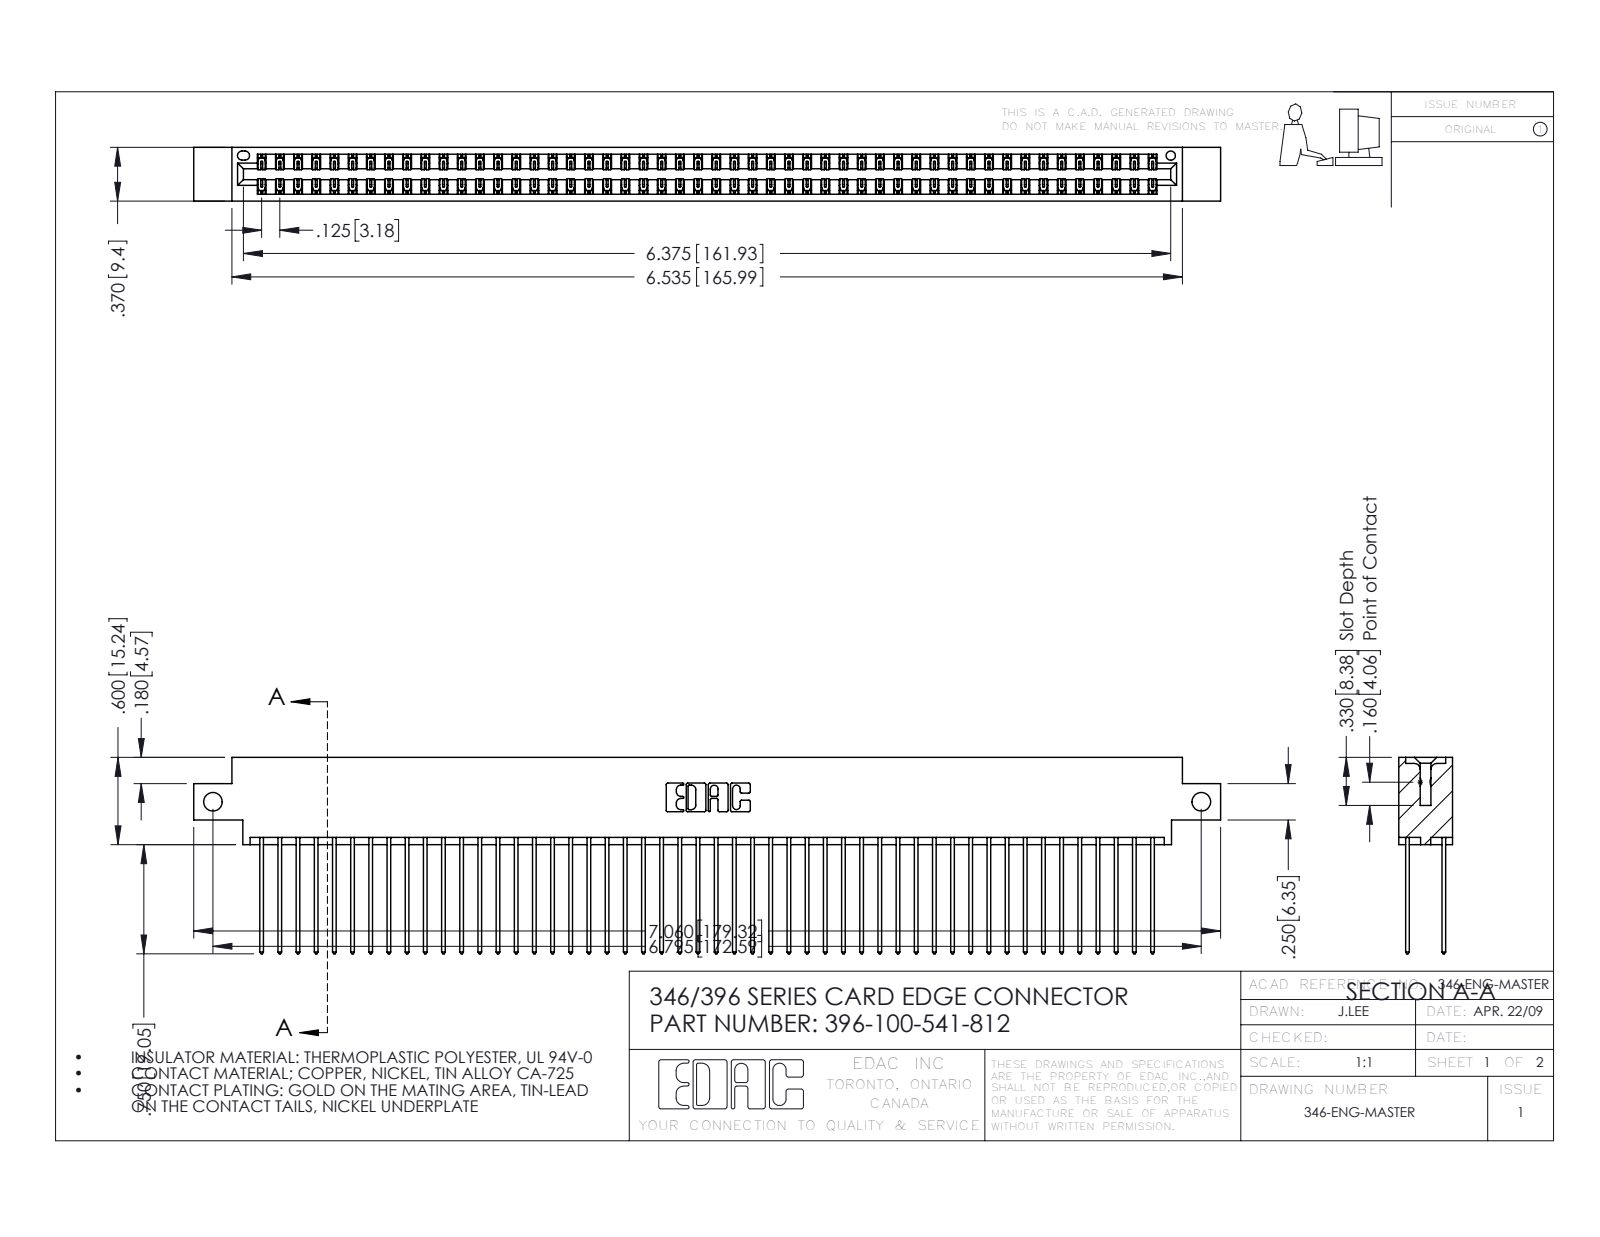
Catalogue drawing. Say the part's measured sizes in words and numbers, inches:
The part is named "346 Part_0.170 Offset - Side Mount; 396-100-541-812; 345-292-001_345-293-141". Its 3-D file was written by "SolidWorks 2016 (CONFIG_CONTROL_DESIGN)". It is 101 solids with 5326 faces: 3580 planar, 1746 cylindrical and 0 other. Overall it measures 7.06 by 1.35 by 0.37 inches. Its volume is 1.091 cubic inches and its surface area 42.62 square inches. Round holes: 2 of diameter 0.128, 1 of diameter 0.064. Partial cylindrical surfaces (rounded edges, fillets, slot ends): 150 of radius 0.006, 100 of radius 0.01, 22 of radius 0.01, 6 of radius 0.007, 6 of radius 0.031, 3 of radius 0.026, 2 of radius 0.014, 2 of radius 0.022. The main face-to-face distances are 0.048, 0.322, 0.25, 0.072, 0.298, 0.025, 0.37, 0.275, 0.225, 0.148. The hole center spacings are 6.795.
